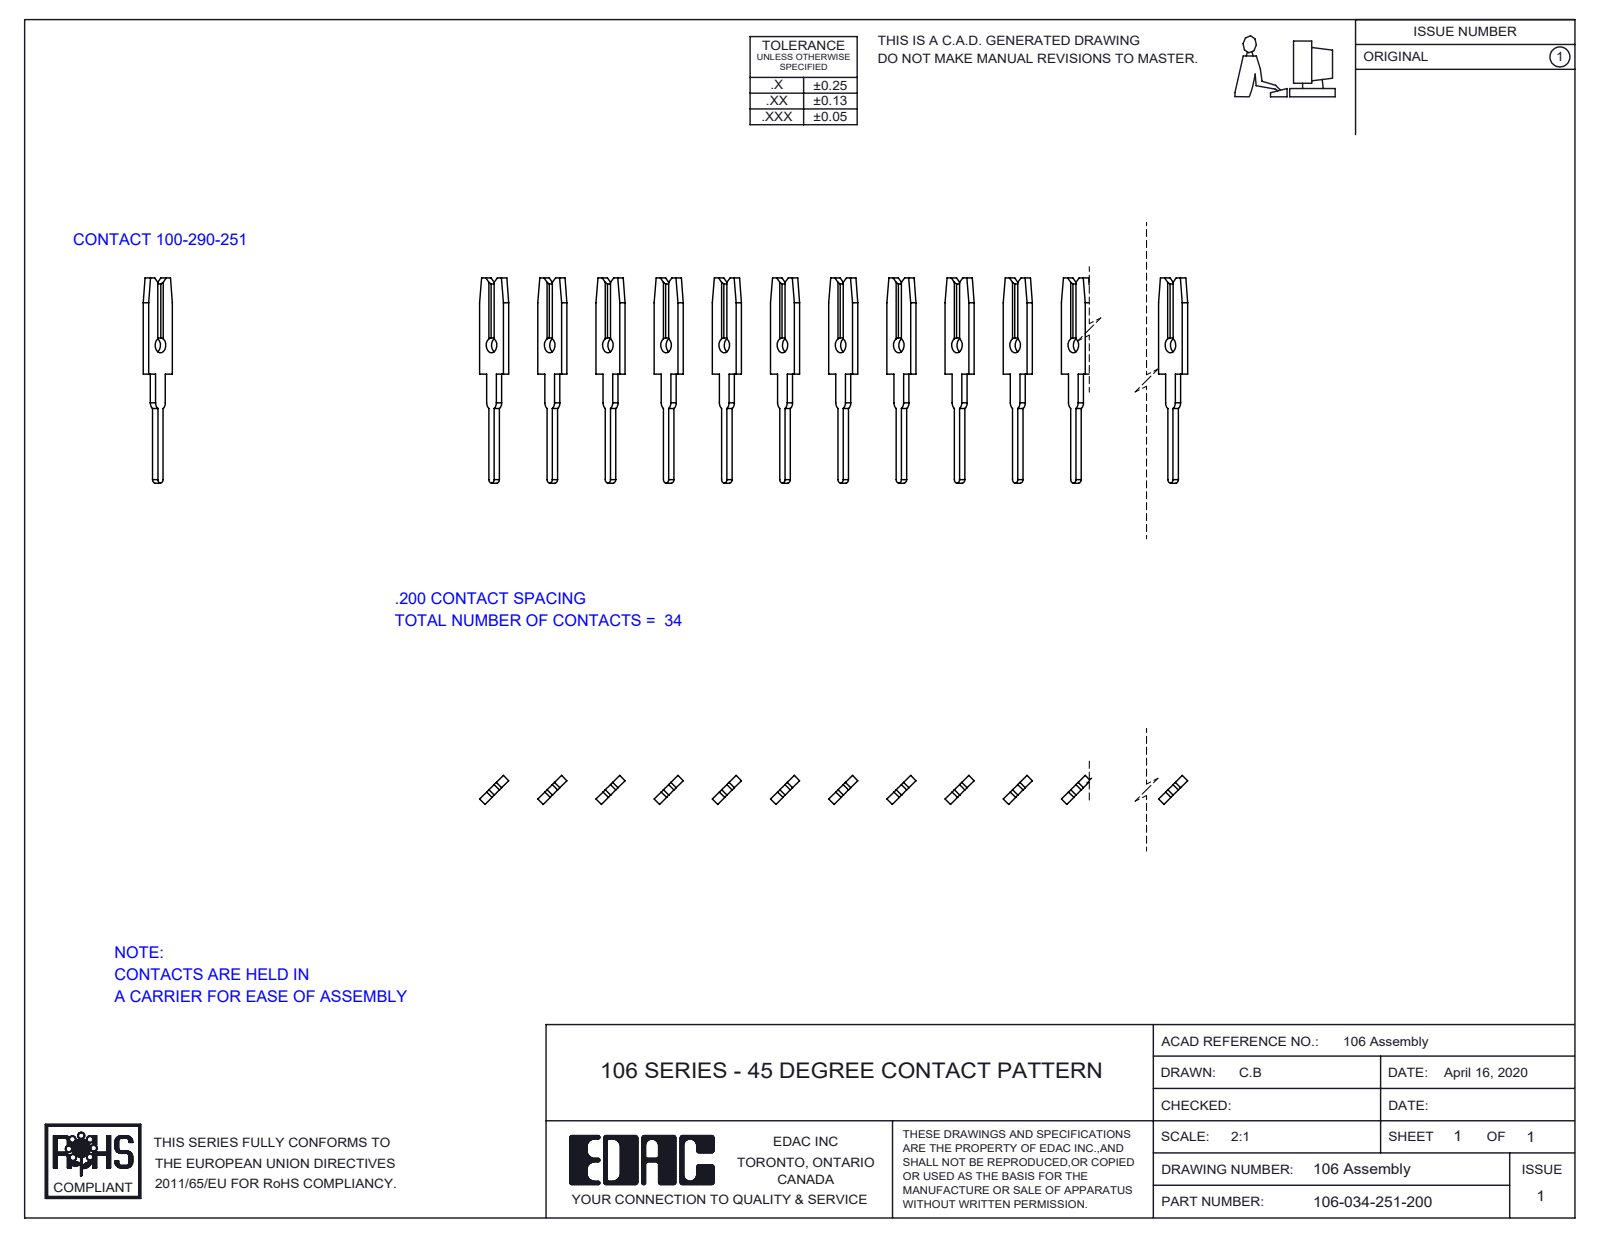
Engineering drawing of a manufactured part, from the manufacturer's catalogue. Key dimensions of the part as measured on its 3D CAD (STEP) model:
Part name (STEP PRODUCT): 100-290-001_100-290-251; 106-034-251-200
STEP written by: SolidWorks 2016 (CONFIG_CONTROL_DESIGN)
Units: inches
Bodies: 34 solids, 952 faces (748 planar, 204 cylindrical, 0 other)
Overall size (bounding box): 6.7 × 0.705 × 0.1
Volume: 0.038 in³ · Surface area: 4.736 in²
Round holes (diameter × count): ⌀0.052 ×34
Partial cylindrical surfaces — rounded edges, fillets, slot ends (radius × count): R0.012 ×34, R0.024 ×34
Main face-to-face distances: 0.141, 0.848, 0.707, 0.283, 0.99, 0.566, 0.424, 1.131, 0.424, 1.556
Hole centre spacings: 0.141, 0.283, 0.424, 0.848, 1.839, 0.99, 1.556, 1.697
